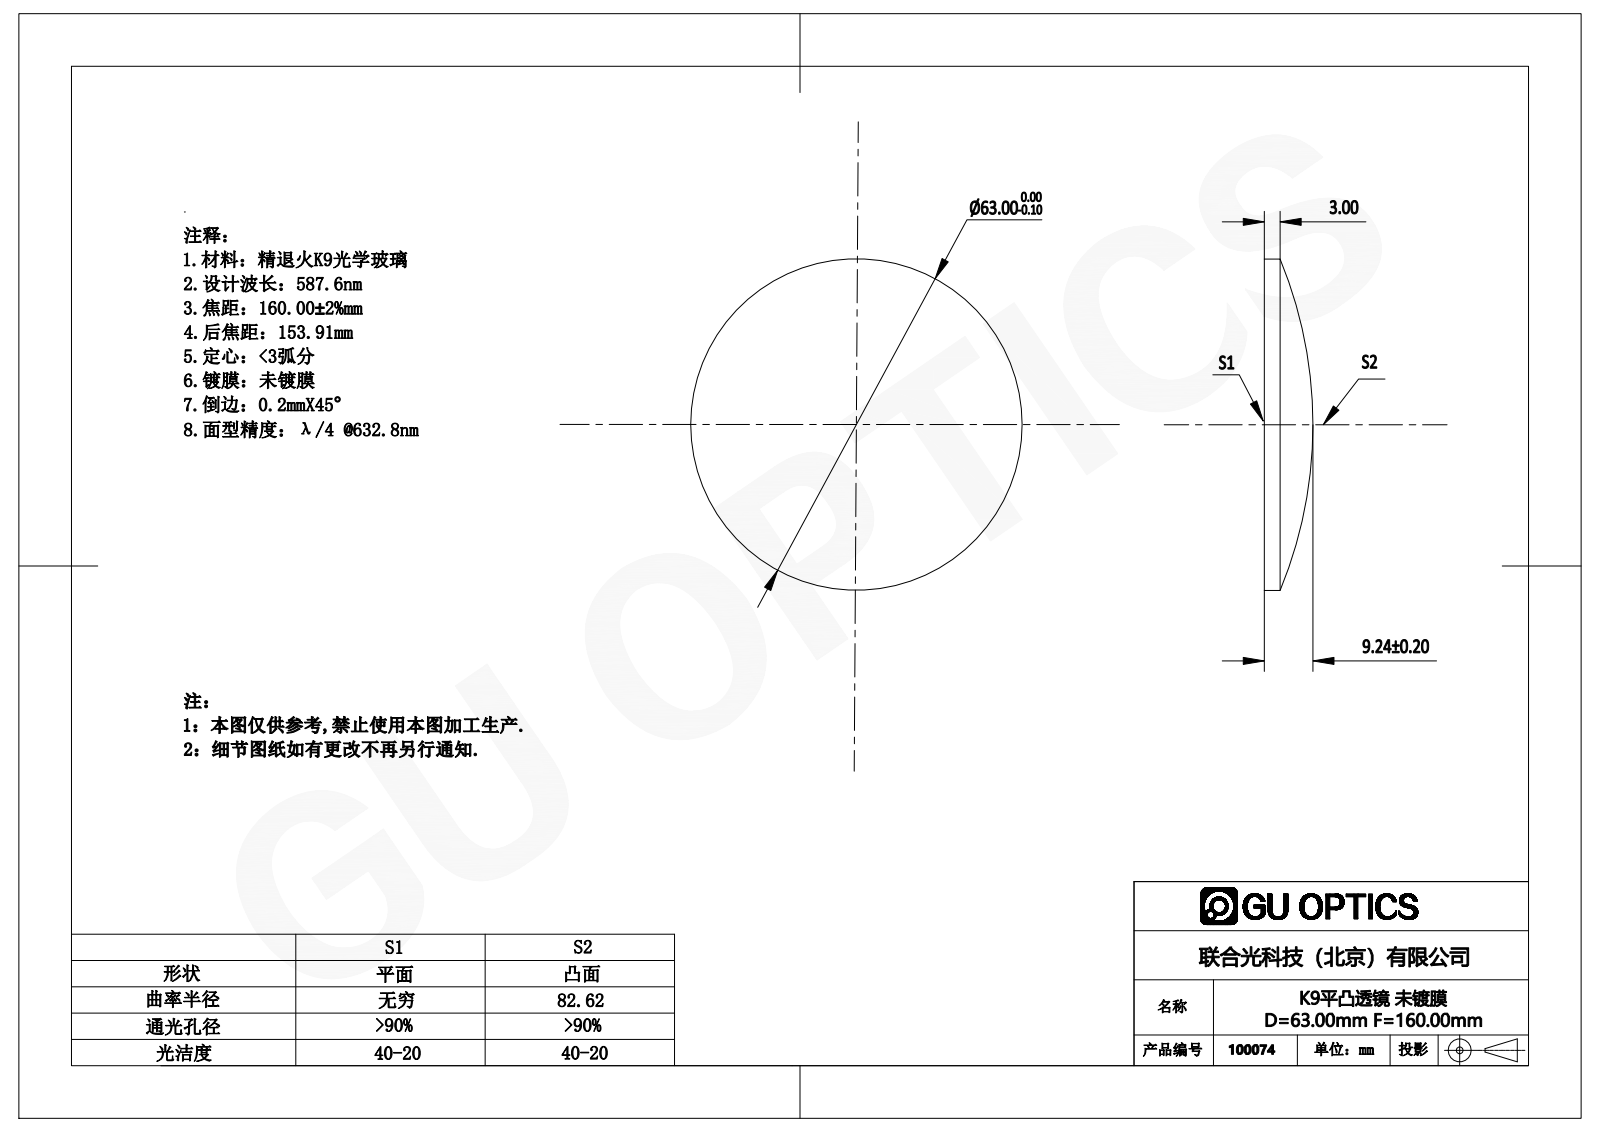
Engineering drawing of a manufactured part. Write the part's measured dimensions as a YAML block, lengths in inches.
part_name: "100074"
step_written_by: "SolidWorks 2016 (AUTOMOTIVE_DESIGN)"
units: inches
bodies: {solids: 1, faces: 5, planar: 1, cylindrical: 2, other: 2}
overall_size: [2.48, 2.48, 0.364]
volume: 1.172
surface_area: 10.77
round_bosses_or_shafts:
  - {diameter: 2.48, count: 1}
